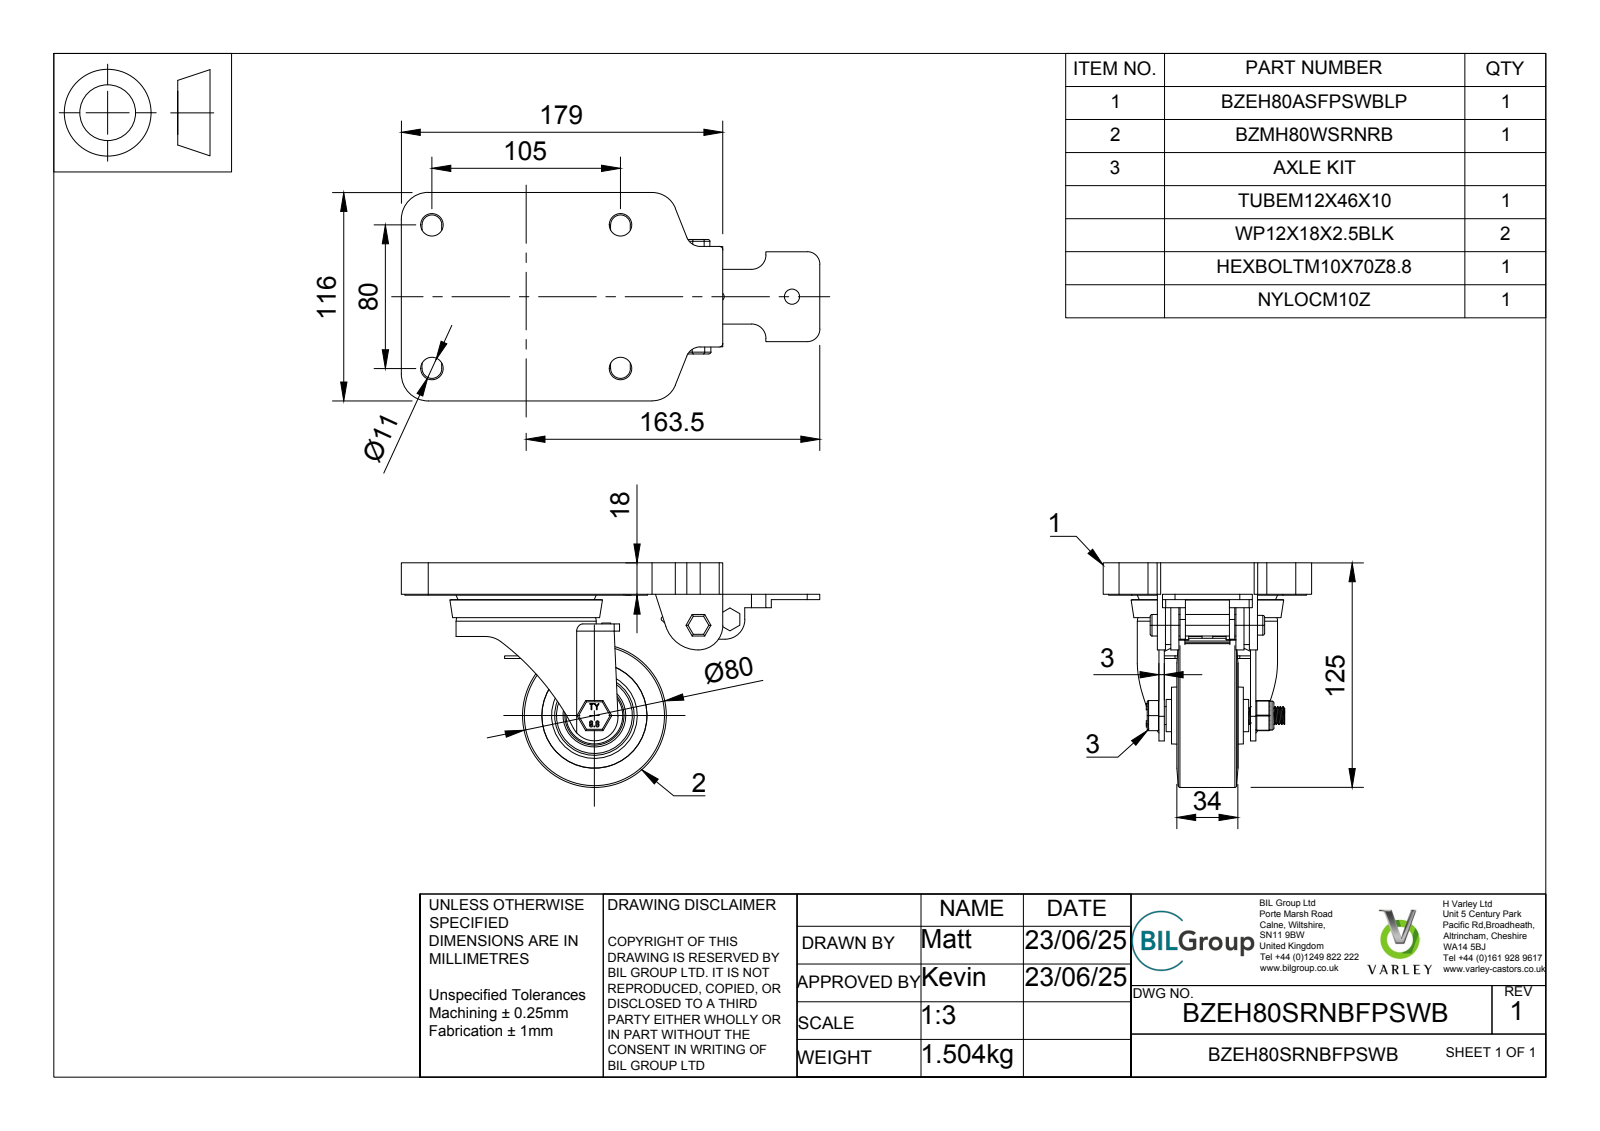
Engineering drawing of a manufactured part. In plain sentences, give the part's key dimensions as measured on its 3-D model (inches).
The part is named "BZEH80SRNBFPSWB v3; BZEH80ASFPSWBLP v1; BZEH100ASFPSWBLP; ZINC PLATED, PRESSED STEEL TOP PLATE (+8 more)". Its 3-D file was written by "Autodesk Translation Framework v14.10.0.0 (AUTOMOTIVE_DESIGN)". It is 33 solids with 797 faces: 446 planar, 273 cylindrical and 78 other. Overall it measures 9.173 by 4.921 by 4.567 inches. Its volume is 36.56 cubic inches and its surface area 328.3 square inches. Round holes: 5 of diameter 0.492, 3 of diameter 0.197, 2 of diameter 0.236, 1 of diameter 0.335, 1 of diameter 0.394, 1 of diameter 0.402, 1 of diameter 0.472, 1 of diameter 0.488, 1 of diameter 0.496, 1 of diameter 0.807, 1 of diameter 0.976, 1 of diameter 0.984. Round bosses or shafts: 8 of diameter 0.148, 2 of diameter 0.787, 1 of diameter 3.15, 1 of diameter 3.071, 1 of diameter 1.988, 1 of diameter 1.22, 1 of diameter 0.969, 1 of diameter 0.709. Partial cylindrical surfaces (rounded edges, fillets, slot ends): 18 of radius 0.02, 14 of radius 0.039, 12 of radius 0.01, 10 of radius 0.079, 8 of radius 0.059, 8 of radius 0.217, 6 of radius 0.03, 5 of radius 0.157. The main face-to-face distances are 0.118, 0.02, 0.138, 0.571, 0.591, 0.256, 0.709, 0.098, 0.236, 0.689. The hole center spacings are 2.598, 1.032, 1.853, 2.187, 2.555, 2.685, 3.15, 3.948.
